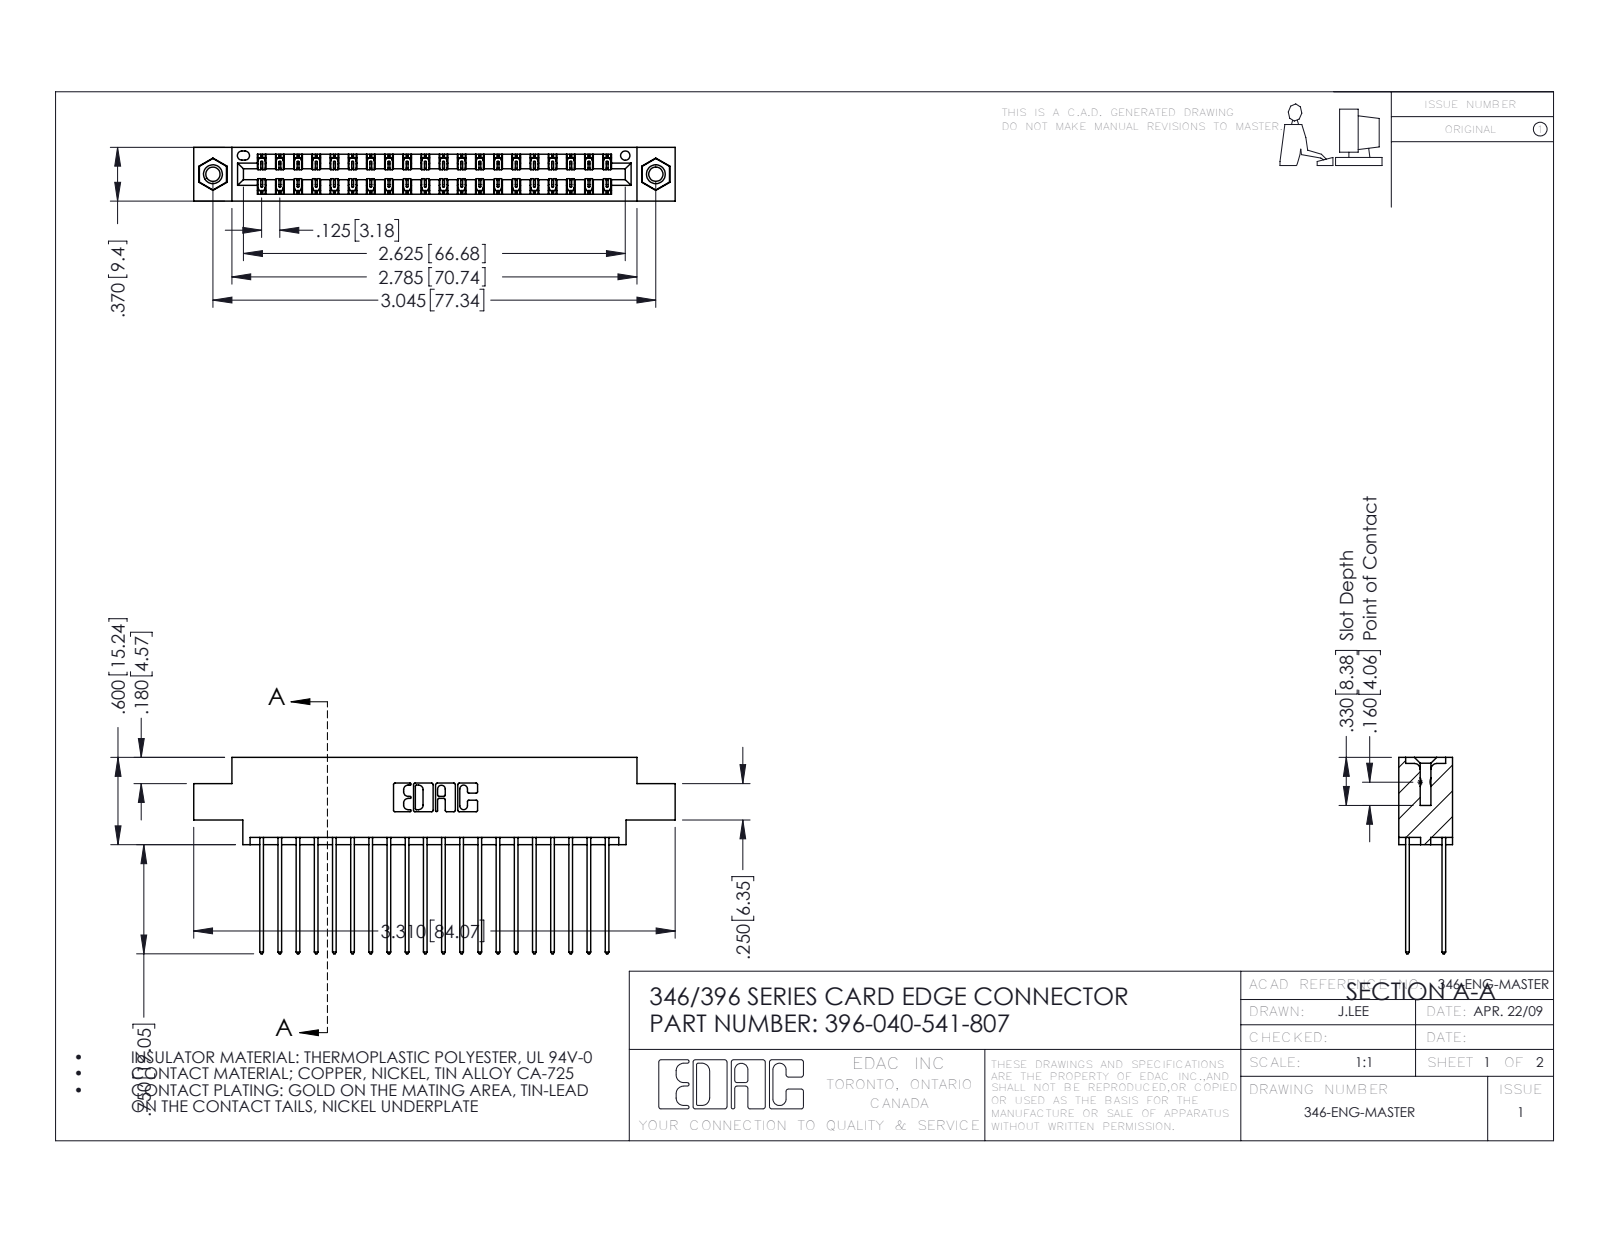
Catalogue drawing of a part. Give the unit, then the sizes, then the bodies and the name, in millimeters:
Units: millimetres
Overall size (bounding box): 84.1 × 34.3 × 9.4
Round holes (diameter × count): ⌀2.5 ×2, ⌀3.2 ×2, ⌀4 ×2, ⌀1.6 ×1
Round bosses / shafts (diameter × count): ⌀3.9 ×2
Partial cylindrical surfaces — rounded edges, fillets, slot ends (radius × count): R0.2 ×60, R0.3 ×40, R0.3 ×22, R0.2 ×6, R0.8 ×6, R0.7 ×3, R0.4 ×2, R0.6 ×2
Main face-to-face distances: 1.2, 8.2, 6.4, 1.8, 7.6, 0.6, 9.4, 7, 5.6, 5.7
Hole centre spacings: 6.2, 72.1, 77.3
Volume: 8 100 mm³ · Surface area: 12 080 mm²
Bodies: 43 solids, 2266 faces (1512 planar, 738 cylindrical, 16 other)
Part name (STEP PRODUCT): 346 Part_0.170 Offset - 0.156 Dia-TI; 396-040-541-807; 345-292-001_345-293-141; 345-250-001_345-250-005-103
STEP written by: SolidWorks 2016 (CONFIG_CONTROL_DESIGN)
